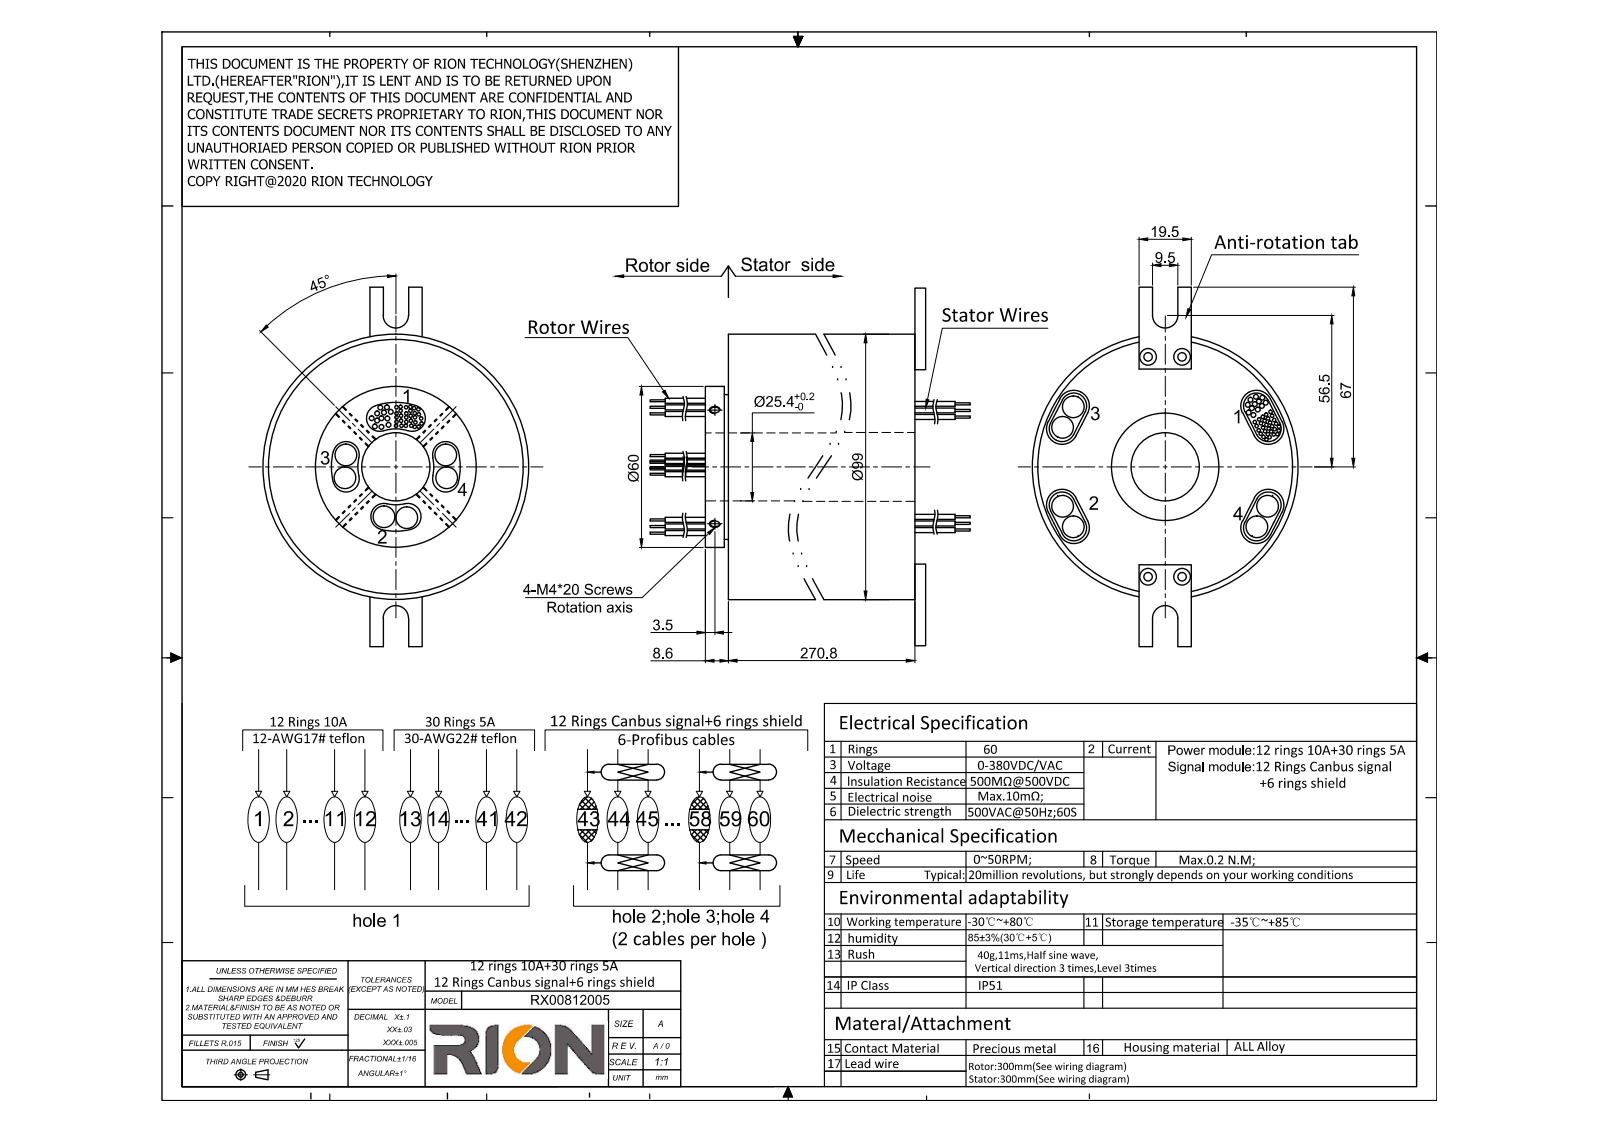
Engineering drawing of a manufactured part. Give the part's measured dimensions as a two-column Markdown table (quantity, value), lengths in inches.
| quantity | value |
| --- | --- |
| part name | RX00812005--RT2599-P1210-P3005-06CAN-SV1 |
| STEP written by | SolidWorks 2014 (CONFIG_CONTROL_DESIGN) |
| units | inches |
| bodies | 1 solid, 432 faces (146 planar, 270 cylindrical, 16 other) |
| overall size | 12.496 × 5.276 × 3.898 |
| volume | 120.9 in³ |
| surface area | 227.4 in² |
| round holes (diameter × count) | 0.098 × 4, 0.126 × 4, 0.13 × 4, 1 × 1, 1.575 × 1, 3.74 × 1 |
| round bosses / shafts (diameter × count) | 0.051 × 59, 0.071 × 24, 0.315 × 12, 3.898 × 1, 3.732 × 1, 2.362 × 1, 2.126 × 1, 1.567 × 1 |
| partial cylindrical surfaces (radius × count) | 0.193 × 8, 0.197 × 8, 0.187 × 2, 0.559 × 1, 0.945 × 1 |
| main face-to-face distances | 10.661, 0.339, 11, 0.157, 11.157, 10.819, 0.748, 11.748, 0.039, 0.276 |
| hole center spacings | 1.633, 0.5, 3.228, 3.267 |
